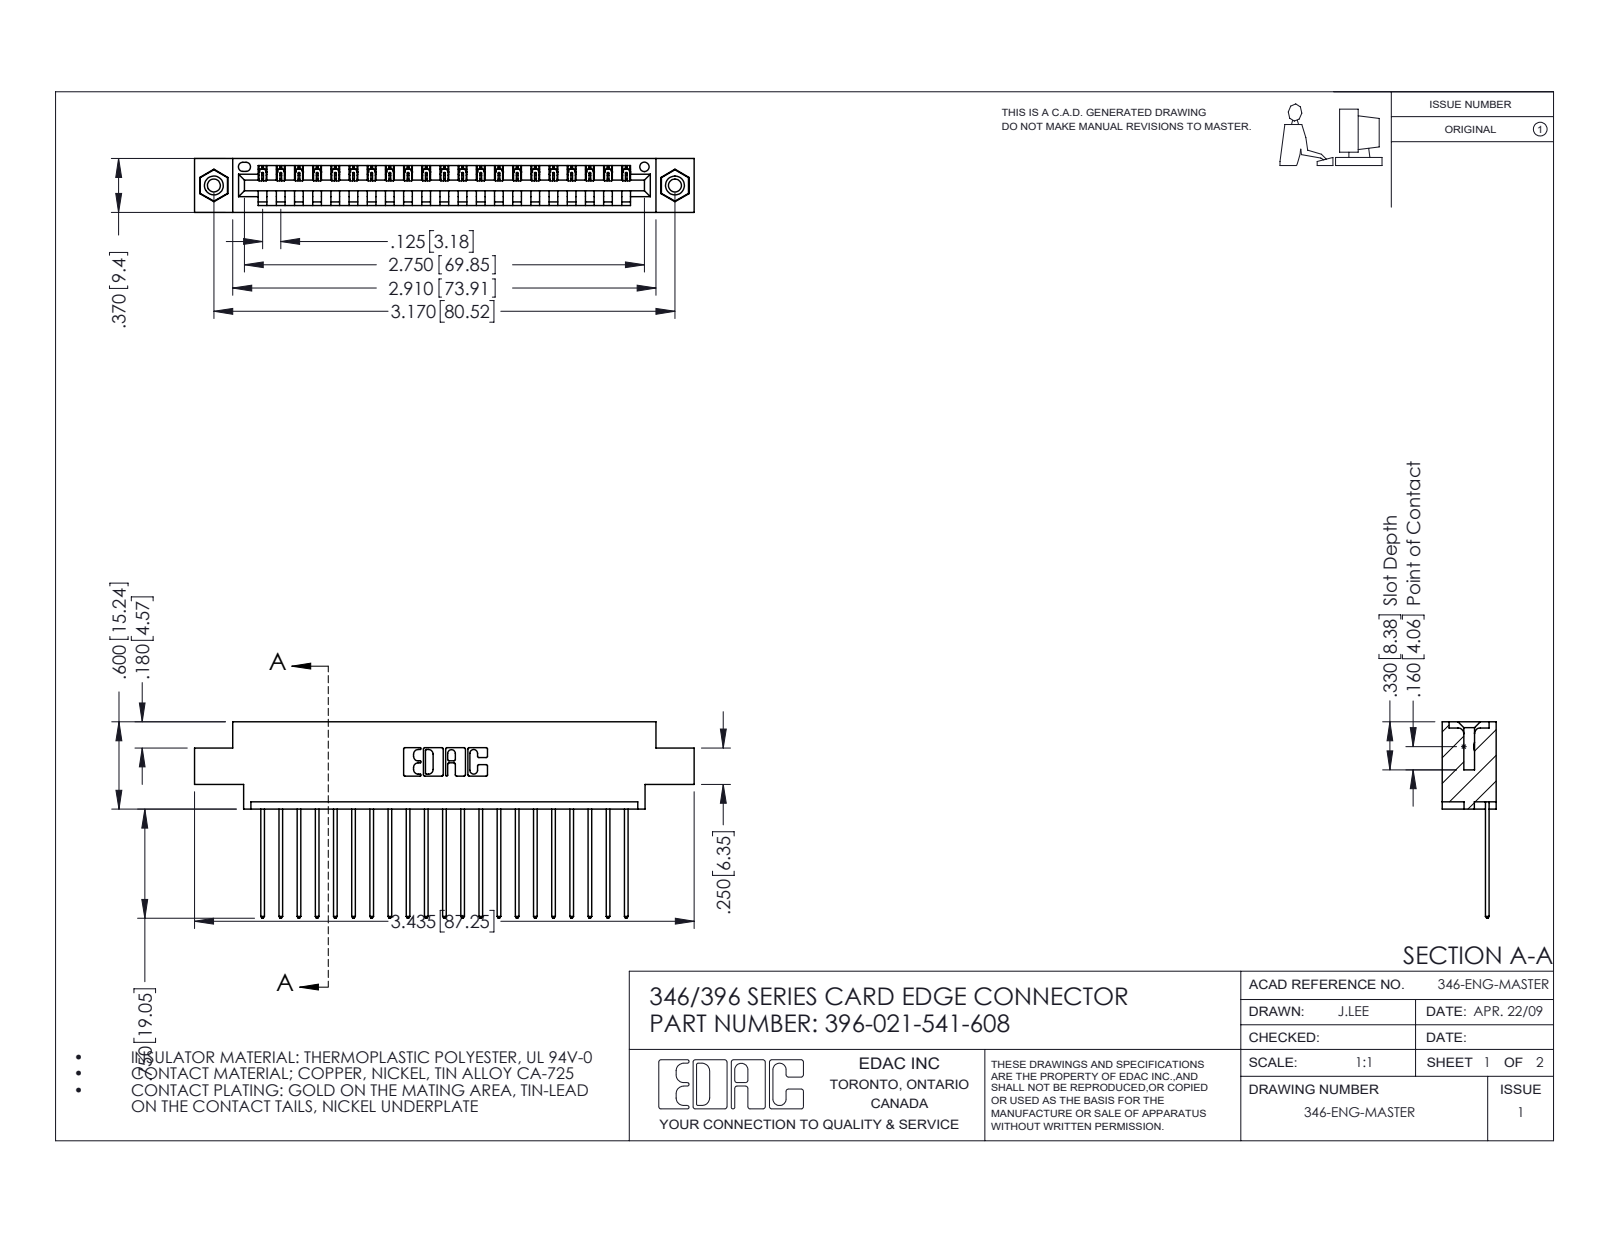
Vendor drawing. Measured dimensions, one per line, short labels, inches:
name: 345-292-001_345-293-141; 396-021-541-608; 346 Part_0.170 Offset - 0.156 Dia-TI; 345-250-001_345-250-003-102
written by: SolidWorks 2016 (CONFIG_CONTROL_DESIGN)
unit: in
bodies: 24 solids, 1404 faces (952 planar, 436 cylindrical, 16 other)
size: 3.435 × 1.35 × 0.37
volume: 0.495 in³; area: 16.29 in²
holes: 2× ⌀0.089, 2× ⌀0.125, 2× ⌀0.156, 1× ⌀0.064
bosses: 2× ⌀0.155
rounds: 42× R0.006, 42× R0.01, 22× R0.01, 6× R0.007, 6× R0.031, 3× R0.026, 2× R0.031, 2× R0.04
face distances: 0.048, 0.322, 0.37, 0.25, 0.072, 0.298, 0.025, 0.222, 0.148, 0.1
hole spacings: 0.246, 2.963, 3.17
